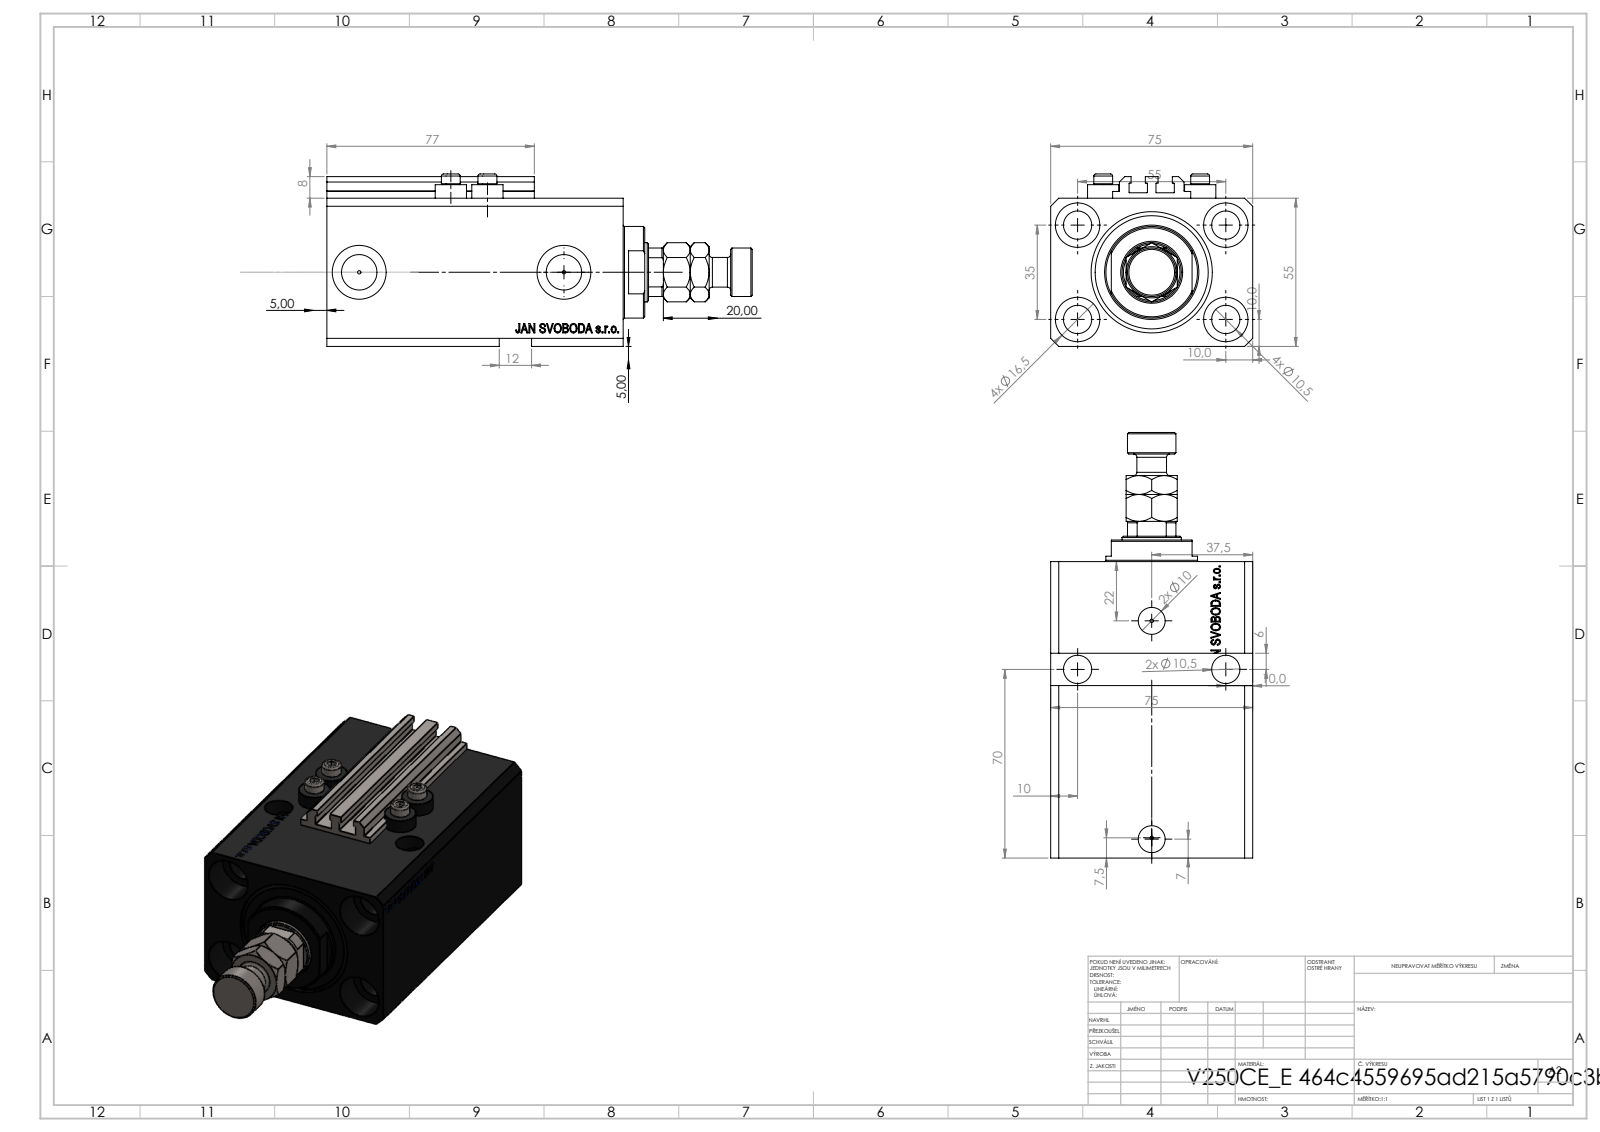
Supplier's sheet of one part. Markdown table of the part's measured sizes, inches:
| quantity | value |
| --- | --- |
| part name | V250CE_E_Body; V250CE_VC_E; MFA; V250CE_C_VCP (+1 more) |
| STEP written by | SolidWorks 2019 (CONFIG_CONTROL_DESIGN) |
| units | inches |
| bodies | 9 solids, 1136 faces (530 planar, 150 cylindrical, 456 other) |
| overall size | 6.22 × 2.953 × 2.52 |
| volume | 23.76 in³ |
| surface area | 152.4 in² |
| round holes (diameter × count) | 0.413 × 9, 0.049 × 4, 0.157 × 4, 0.65 × 4, 0.394 × 2, 0.518 × 2, 0.787 × 2, 0.866 × 1, 1.26 × 1, 1.772 × 1 |
| round bosses / shafts (diameter × count) | 0.457 × 4, 0.276 × 4, 1.339 × 1, 0.709 × 1, 0.433 × 1 |
| partial cylindrical surfaces (radius × count) | 0.008 × 10, 0.413 × 1 |
| main face-to-face distances | 2.165, 2.953, 0.591, 4.331, 3.74, 0.118, 0.39, 3.35, 3.941, 0.098 |
| hole center spacings | 1.283, 1.294, 2.165, 2.706, 0.535, 0.555, 0.907, 1.016 |
